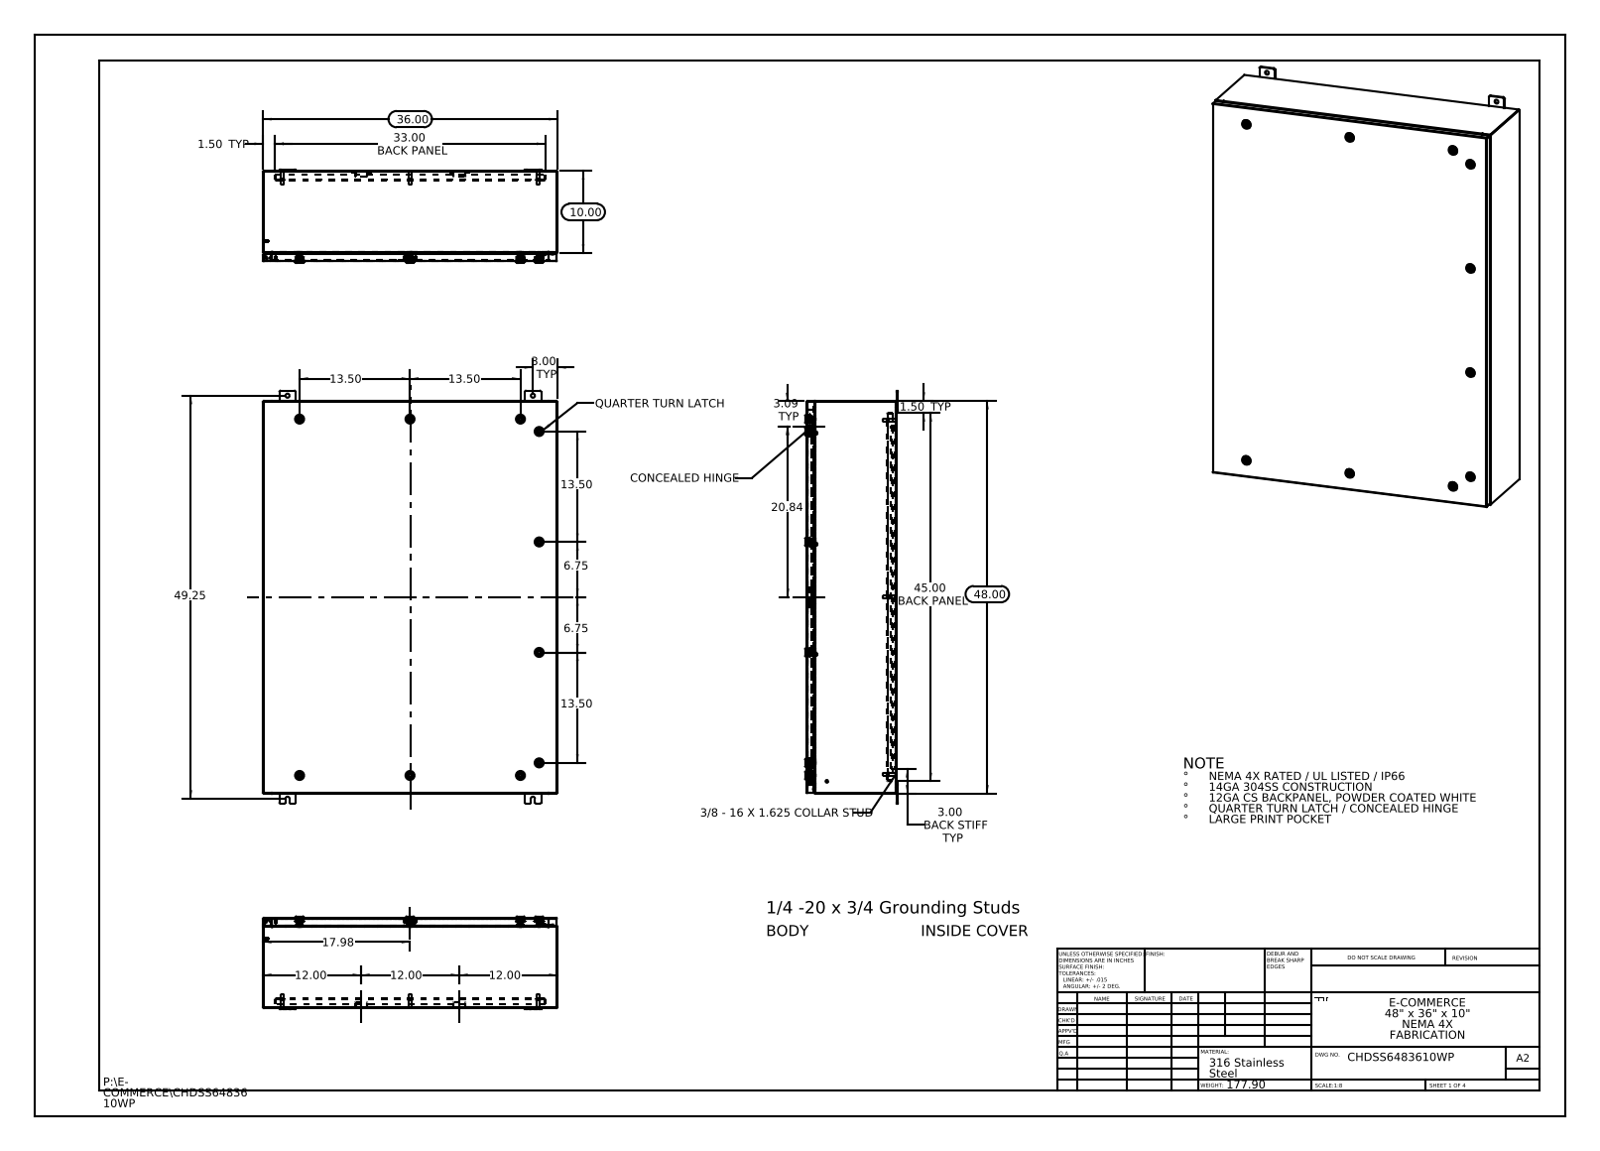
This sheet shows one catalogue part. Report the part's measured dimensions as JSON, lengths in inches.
{"part_name": "Washer-221320-IB-Industrilas_Washer-221320-IB-Industrilas; CHDSS6483610WP Top; CHDSS6483610WP Mounting Studs; CHDSS6483610WP Body (+8 more)", "step_written_by": "SolidWorks 2013 (CONFIG_CONTROL_DESIGN)", "units": "inches", "bodies": {"solids": 94, "faces": 9060, "planar": 2626, "cylindrical": 2826, "other": 3608}, "overall_size": [50.5, 36, 11.356], "volume_in3": 628.3, "surface_area_in2": 15572, "round_holes": [[0.5, 12], [0.197, 10], [0.394, 10], [0.4, 10], [0.63, 10], [0.787, 10], [0.136, 6], [0.25, 6], [0.211, 1]], "round_bosses_or_shafts": [[0.236, 12], [1.102, 10], [0.78, 10], [0.626, 10], [0.61, 10], [0.531, 10], [0.392, 10], [0.114, 10]], "partial_cylinders_radius": [[0.006, 330], [0.118, 330], [0.028, 120], [0.02, 40], [0.197, 40], [0.013, 34], [0.088, 30], [0.19, 24]], "face_to_face_distances": [0.075, 0.074, 10.861, 10.936, 11.01, 10.935, 0.104, 1, 1.075, 9.861], "hole_center_spacings": [13.5, 20, 20.123, 21.625, 27, 38.003, 45.594, 45.986]}
